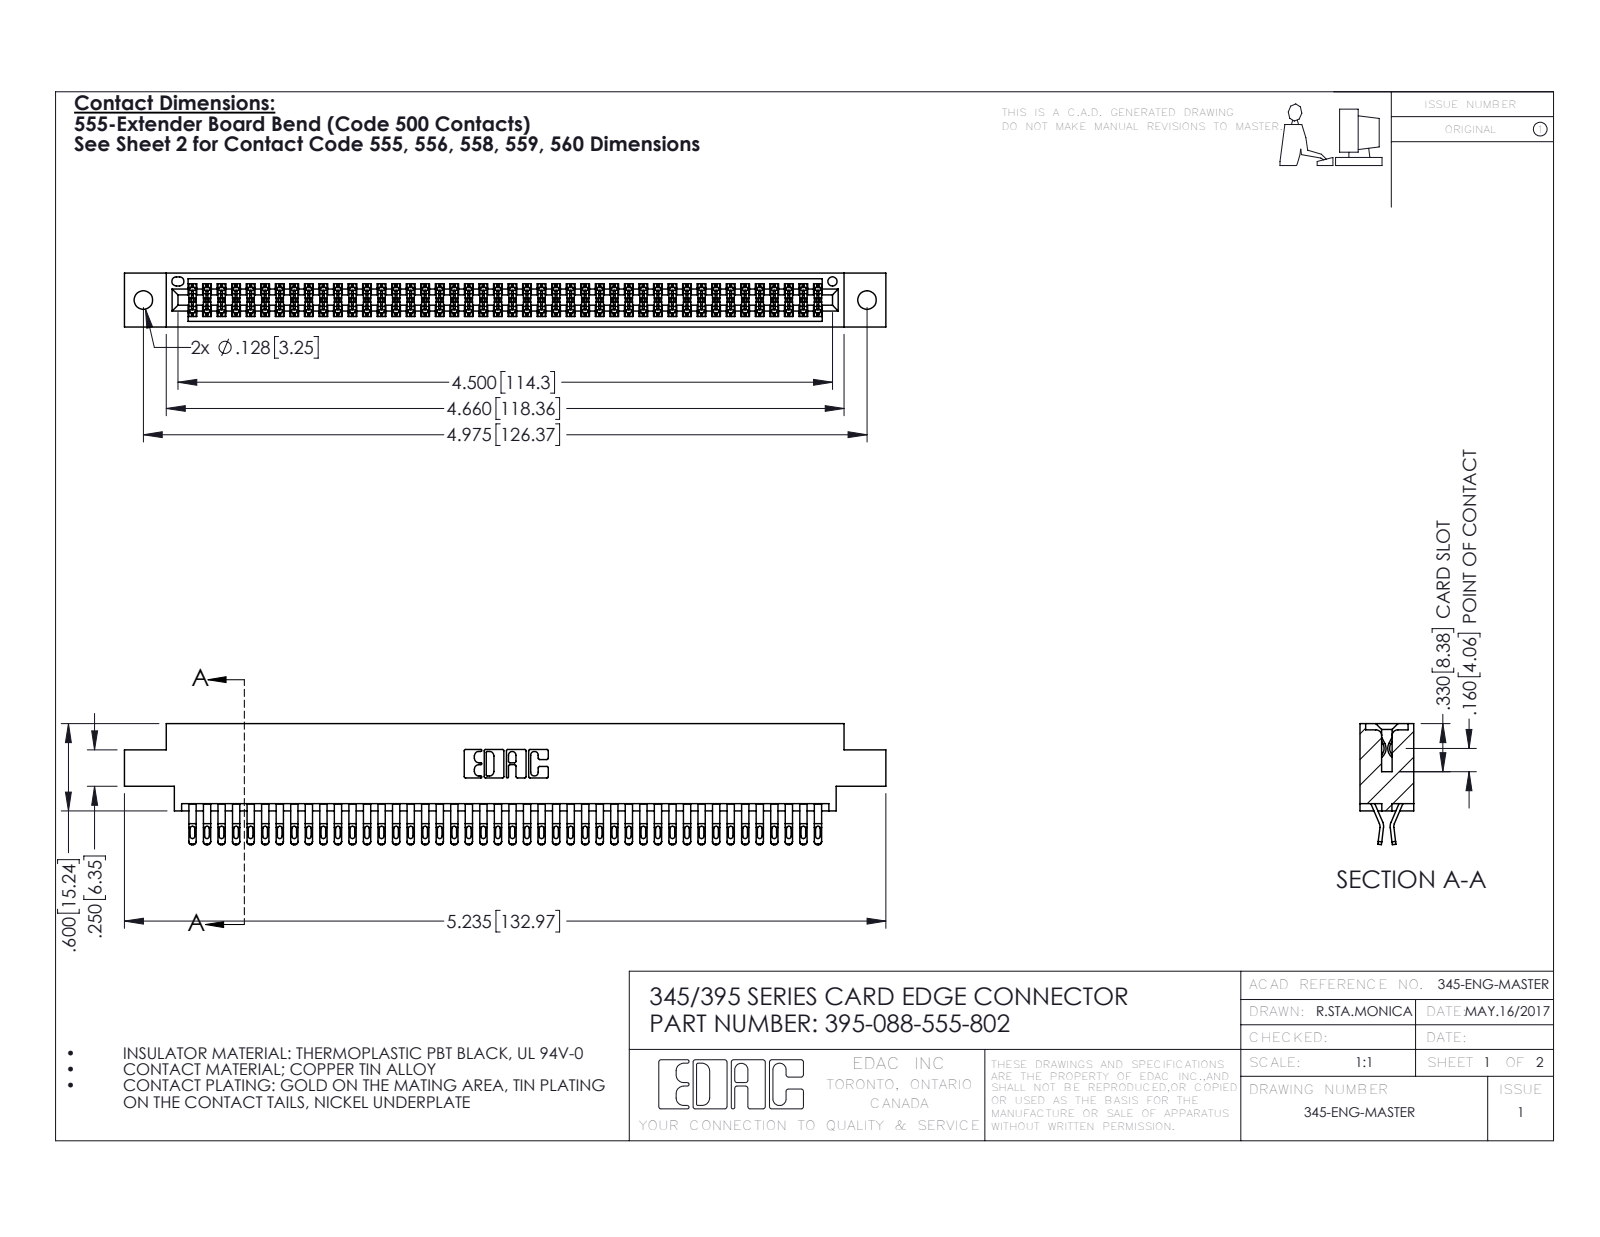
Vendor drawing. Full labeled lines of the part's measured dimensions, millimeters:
Part name (STEP PRODUCT): 395-088-555-802; 345-292-001_555 Tail; 345 Part_0.170 Offset - 0.128 Dia
STEP written by: SolidWorks 2016 (CONFIG_CONTROL_DESIGN)
Units: millimetres
Bodies: 89 solids, 5058 faces (2812 planar, 2246 cylindrical, 0 other)
Overall size (bounding box): 133 × 21.1 × 9.4
Volume: 13 000 mm³ · Surface area: 20 070 mm²
Round holes (diameter × count): ⌀3.3 ×2, ⌀1.6 ×1
Partial cylindrical surfaces — rounded edges, fillets, slot ends (radius × count): R0.4 ×220, R0.5 ×176, R0.2 ×132, R0.3 ×22, R0.2 ×6, R0.8 ×6, R0.7 ×3, R0.3 ×2
Main face-to-face distances: 7.6, 1.8, 9.4, 0.6, 5.1, 2.5, 6.9, 5.7, 4.4, 3.8
Hole centre spacings: 6.9, 120.4, 126.4
